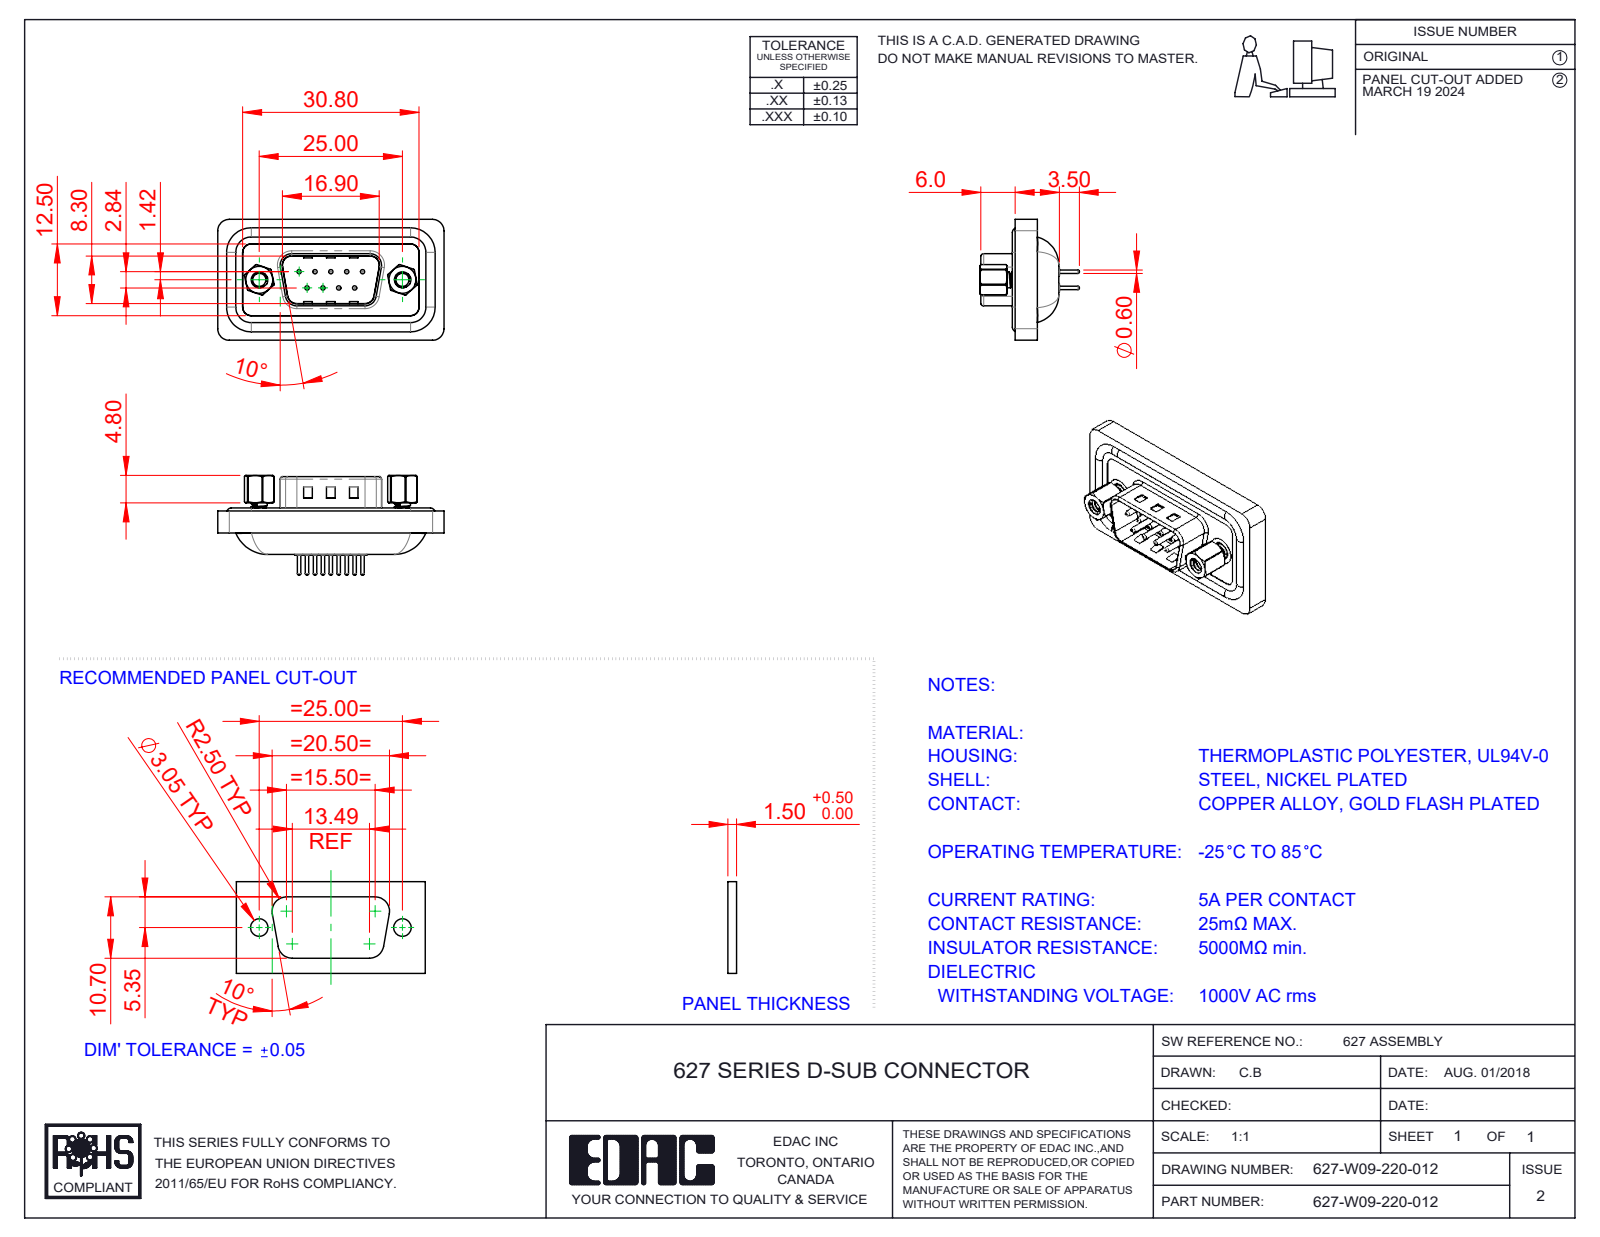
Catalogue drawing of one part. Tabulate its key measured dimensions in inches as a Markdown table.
| quantity | value |
| --- | --- |
| part name | 627W Shell Front_09 Contacts; 627W Waterproof Housing_09 Contacts; 627W Contact Row 1_20; 627-W09-220-012 (+4 more) |
| STEP written by | SolidWorks 2020 (CONFIG_CONTROL_DESIGN) |
| units | inches |
| bodies | 17 solids, 799 faces (204 planar, 356 cylindrical, 239 other) |
| overall size | 1.555 × 0.831 × 0.677 |
| volume | 0.285 in³ |
| surface area | 10.2 in² |
| round holes (diameter × count) | 0.03 × 9, 0.059 × 9, 0.063 × 9, 0.079 × 9, 0.089 × 2, 0.09 × 2, 0.157 × 2, 0.189 × 2, 0.197 × 2 |
| round bosses / shafts (diameter × count) | 0.024 × 9, 0.063 × 4, 0.193 × 2, 0.11 × 2 |
| partial cylindrical surfaces (radius × count) | 0.079 × 16, 0.059 × 14, 0.02 × 8, 0.106 × 6, 0.035 × 4, 0.063 × 4, 0.169 × 4, 0.016 × 2 |
| main face-to-face distances | 0.016, 0.03, 0.043, 0.108, 0.148, 0.02, 0.039, 0.138, 0.073, 0.063 |
| hole center spacings | 0.124, 0.109, 0.218, 0.198, 0.198, 0.327, 0.28, 0.294 |
